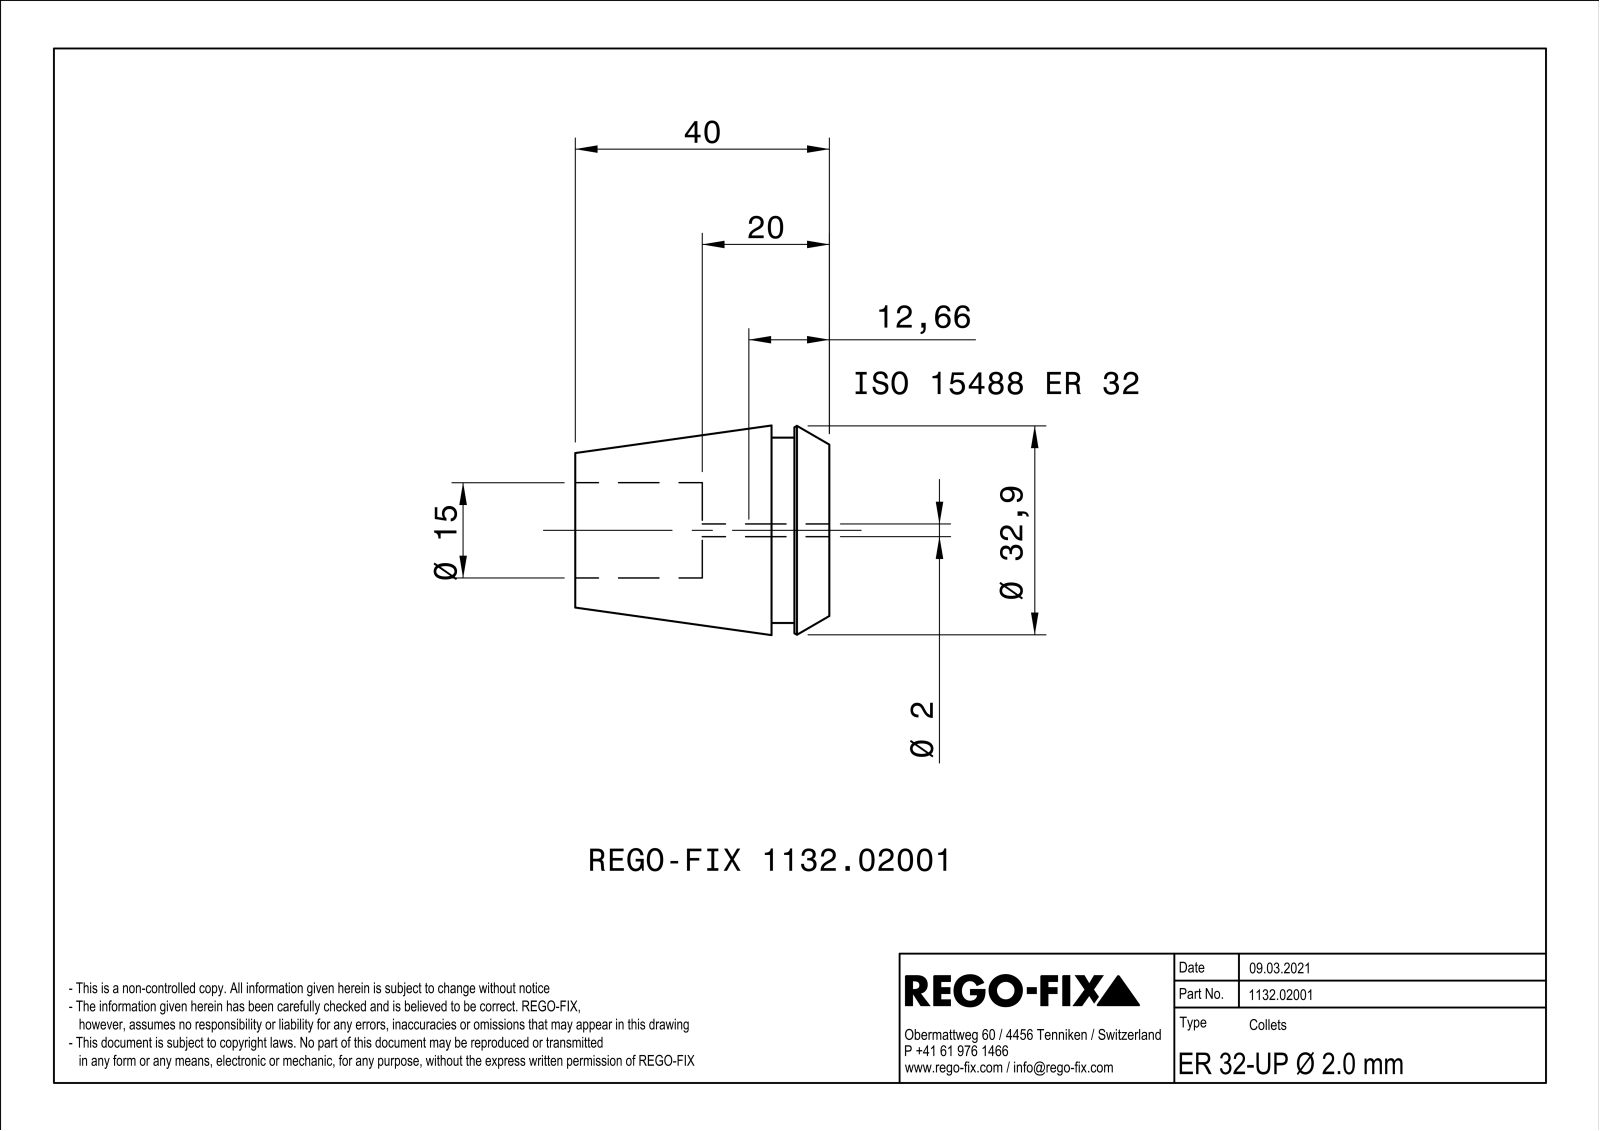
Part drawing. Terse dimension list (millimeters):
name: NOCUT
written by: SIEMENS PLM Software Solid Edge ST10 (AUTOMOTIVE_DESIGN)
unit: mm
bodies: 1 solid, 268 faces (100 planar, 56 cylindrical, 112 other)
size: 40 × 32.99 × 32.99
volume: 19 120 mm³; area: 14 798 mm²
holes: 1× ⌀15
bosses: 1× ⌀29.2
rounds: 14× R0.4, 8× R40, 1× R1
face distances: 0.8, 0.78, 0.82, 0.63, 40, 20, 9.1, 30.9, 5.5, 3.6
